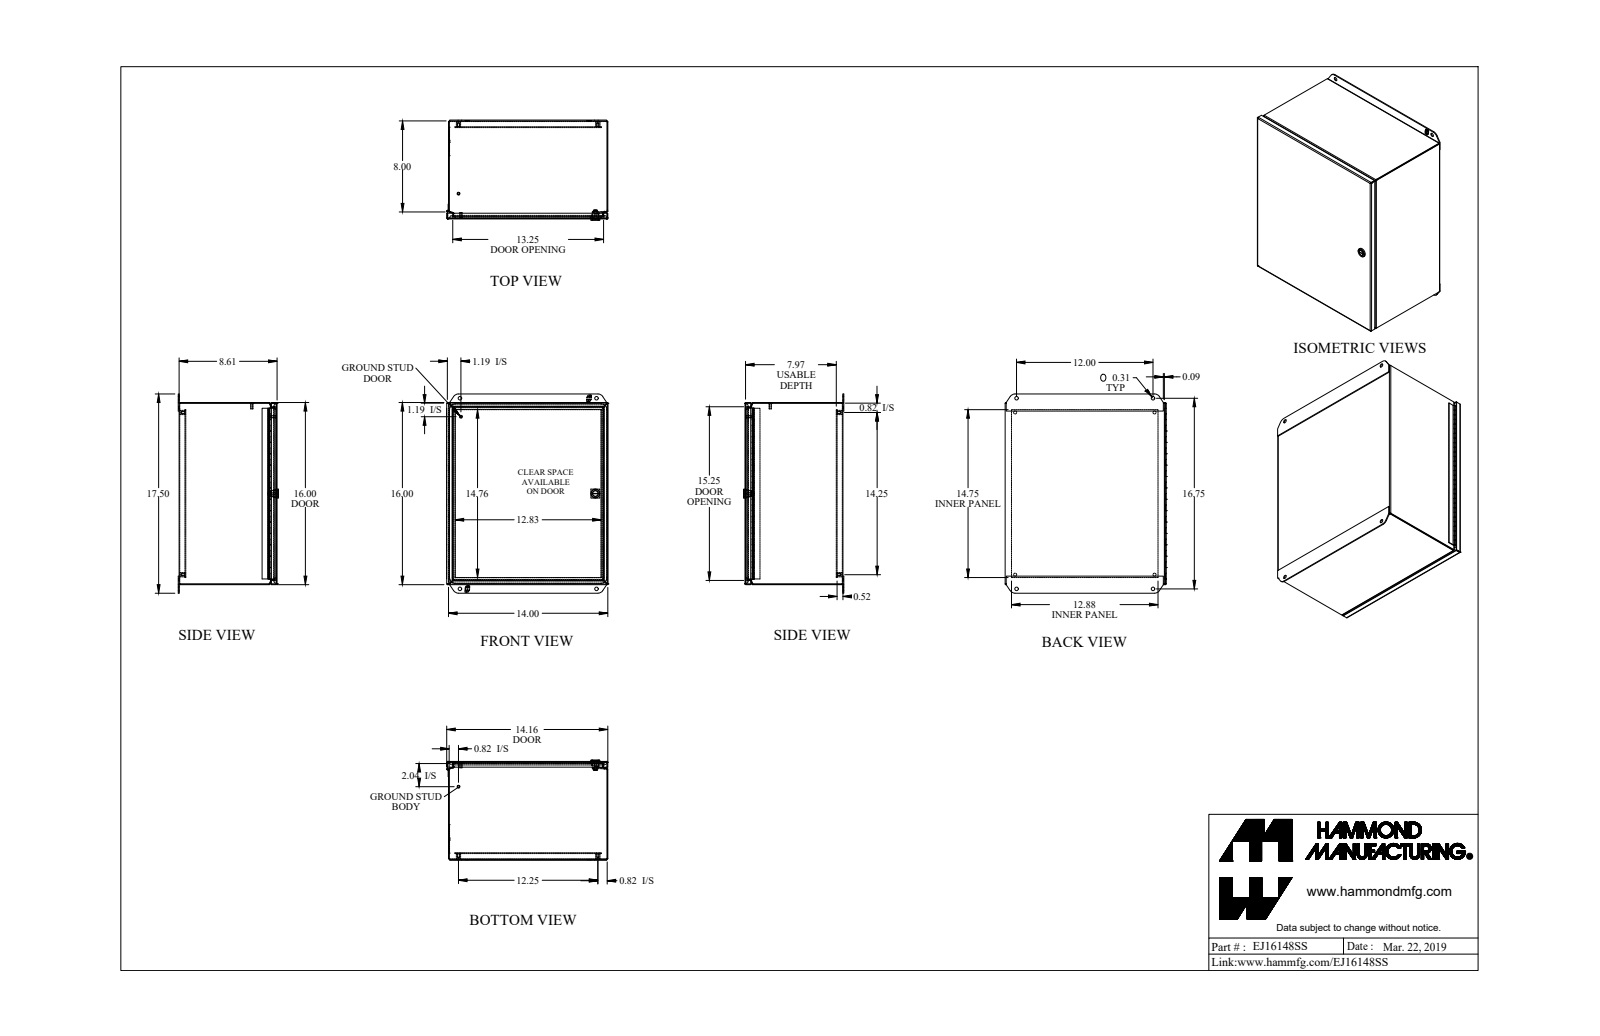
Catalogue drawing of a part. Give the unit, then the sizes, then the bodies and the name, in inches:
Units: inches
Overall size (bounding box): 17.5 × 14.165 × 8.805
Round holes (diameter × count): ⌀0.156 ×4, ⌀0.265 ×4, ⌀0.313 ×4, ⌀0.05 ×1, ⌀0.516 ×1
Round bosses / shafts (diameter × count): ⌀0.375 ×4, ⌀0.25 ×2, ⌀0.19 ×2, ⌀0.788 ×1, ⌀0.535 ×1, ⌀0.496 ×1, ⌀0.435 ×1, ⌀0.1 ×1
Partial cylindrical surfaces — rounded edges, fillets, slot ends (radius × count): R0.029 ×16, R0.086 ×16, R0.281 ×12, R0.25 ×4, R0.499 ×4, R0.5 ×4, R0.06 ×2, R0.03 ×1
Main face-to-face distances: 0.057, 8.554, 13.943, 0.072, 0.589, 15.943, 8.611, 8.497, 8.094, 8.037
Hole centre spacings: 1.257, 12.189, 15.5, 19.679, 7.128, 8.376, 12, 12.25
Volume: 79.6 in³ · Surface area: 2 640 in²
Bodies: 16 solids, 784 faces (434 planar, 254 cylindrical, 96 other)
Part name (STEP PRODUCT): EJ16148SS_Default
STEP written by: SolidWorks 2019 (CONFIG_CONTROL_DESIGN)
